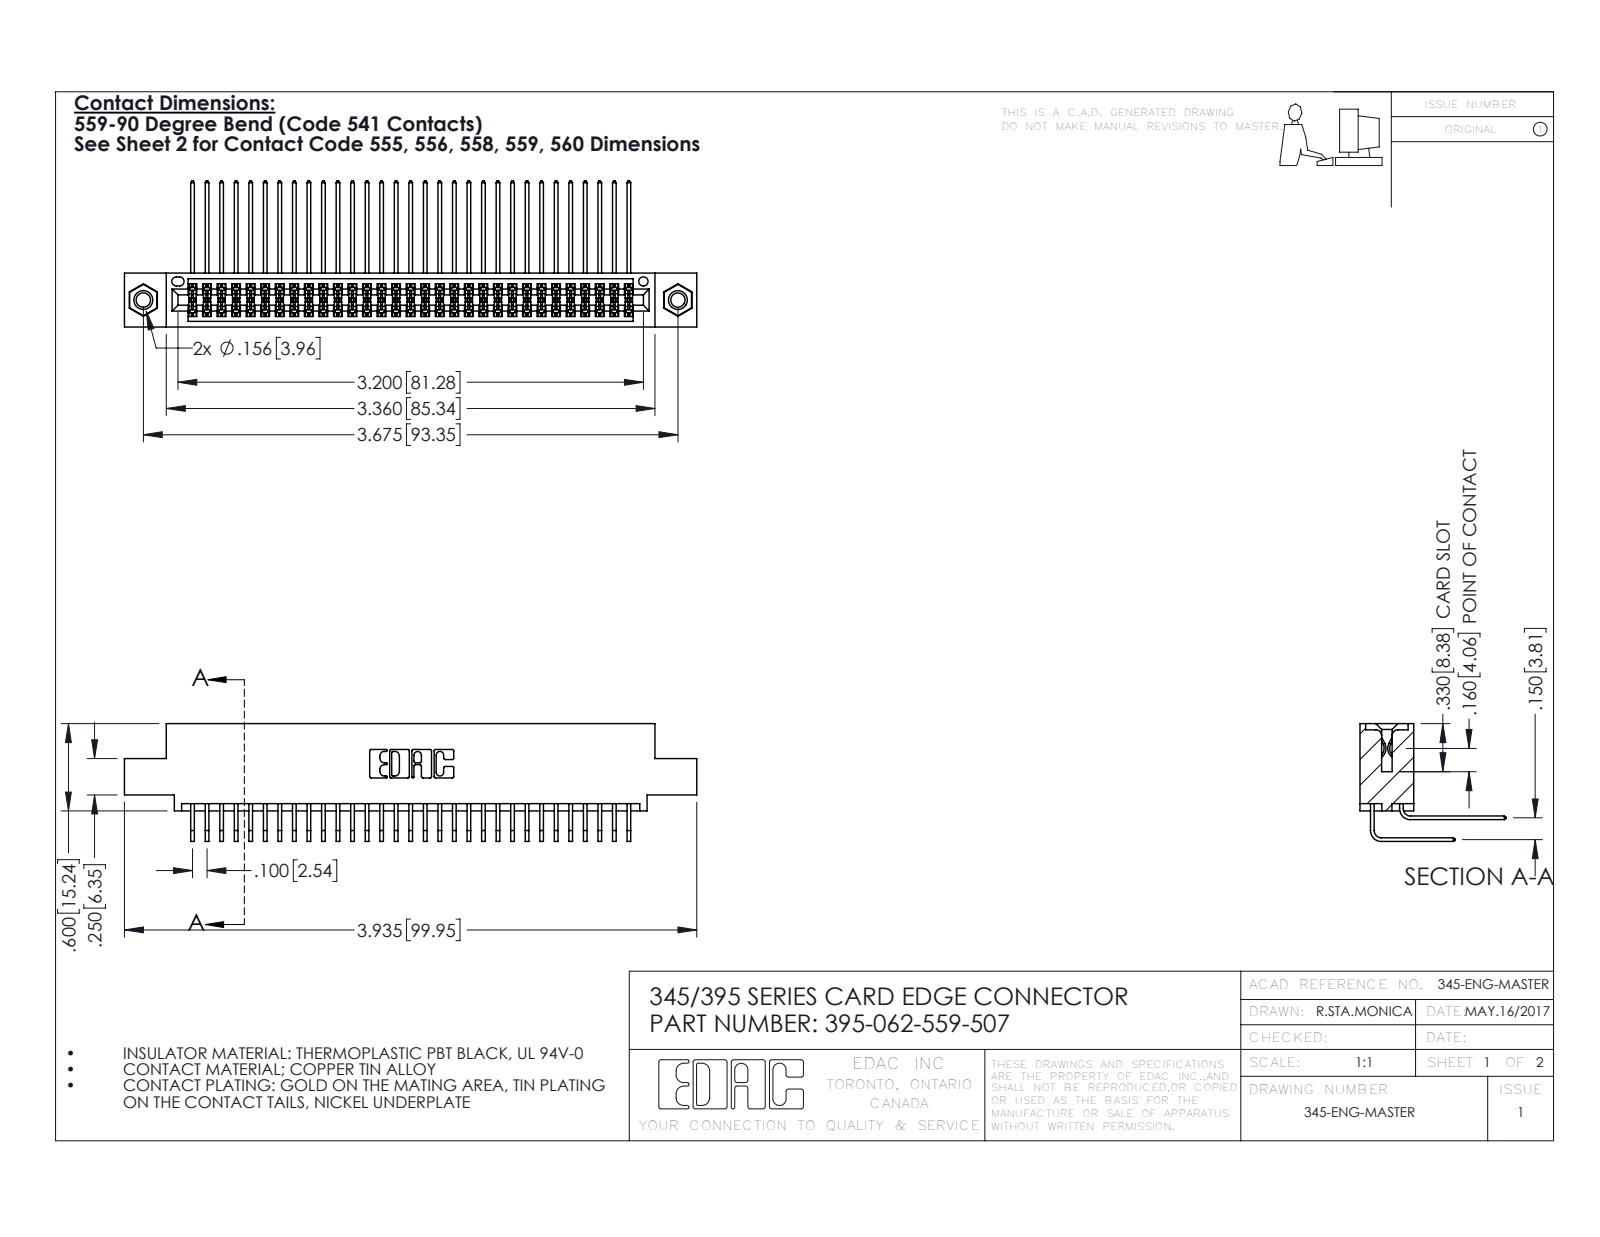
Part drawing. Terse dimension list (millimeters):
name: 345-250-001_345-250-005-103; 345-292-001_558 559 Tail - 1; 345 Part_0.110 Offset - 0.156 Dia-TI; 345-292-001_559 Tail - 2 (+1 more)
written by: SolidWorks 2016 (CONFIG_CONTROL_DESIGN)
unit: mm
bodies: 65 solids, 3414 faces (2286 planar, 1112 cylindrical, 16 other)
size: 99.9 × 25.5 × 20.5
volume: 9 880 mm³; area: 16 190 mm²
holes: 2× ⌀2.5, 2× ⌀3.2, 2× ⌀4, 1× ⌀1.6
bosses: 2× ⌀3.9
rounds: 93× R0.2, 22× R0.3, 6× R0.2, 6× R0.8, 3× R0.7, 2× R0.4, 2× R0.5, 2× R0.6
face distances: 1.8, 7.6, 5.1, 9.4, 2.5, 6.9, 0.6, 5.7, 3.8, 4.4
hole spacings: 6.9, 87.4, 93.3
